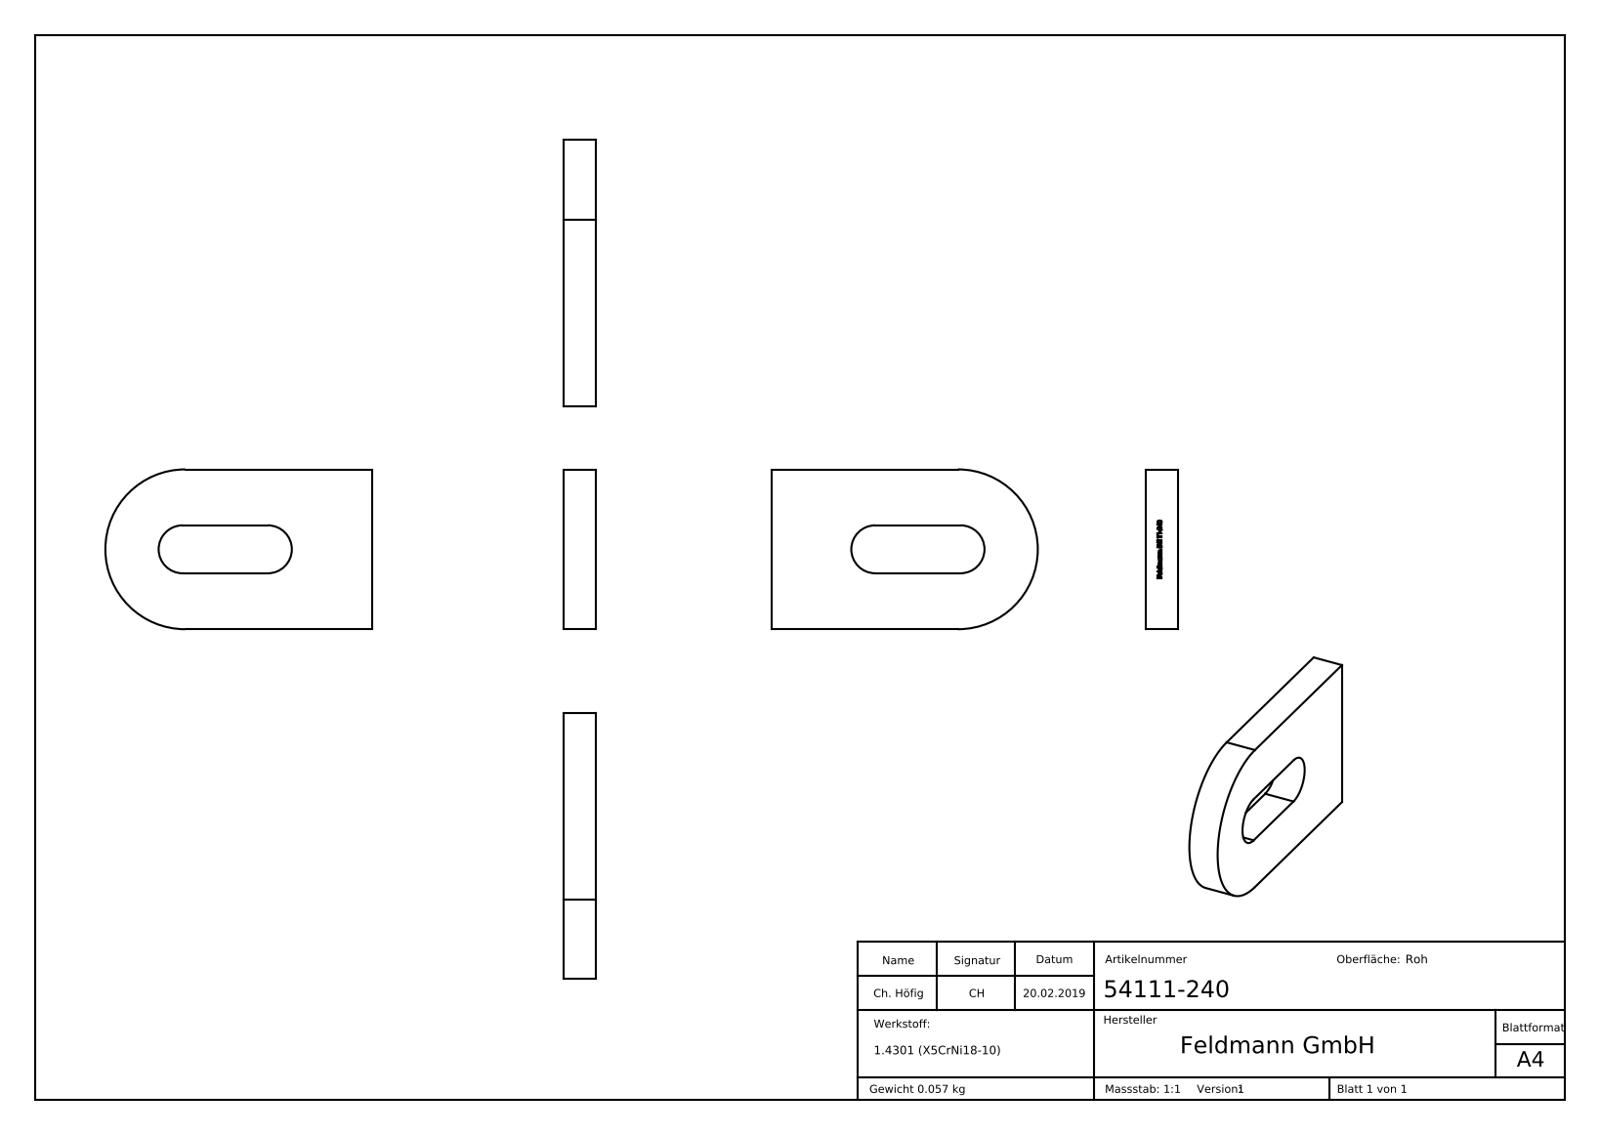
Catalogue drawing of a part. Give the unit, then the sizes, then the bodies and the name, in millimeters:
Units: millimetres
Overall size (bounding box): 50 × 30 × 6
Partial cylindrical surfaces — rounded edges, fillets, slot ends (radius × count): R4.5 ×2, R15 ×1
Main face-to-face distances: 6, 30, 10.5, 19.5, 9, 3, 0.61, 0.53, 2.82, 0.36
Volume: 7 175 mm³ · Surface area: 3 641 mm²
Bodies: 1 solid, 220 faces (144 planar, 5 cylindrical, 71 other)
Part name (STEP PRODUCT): 54111-240
STEP written by: SolidWorks 2015 (CONFIG_CONTROL_DESIGN)
